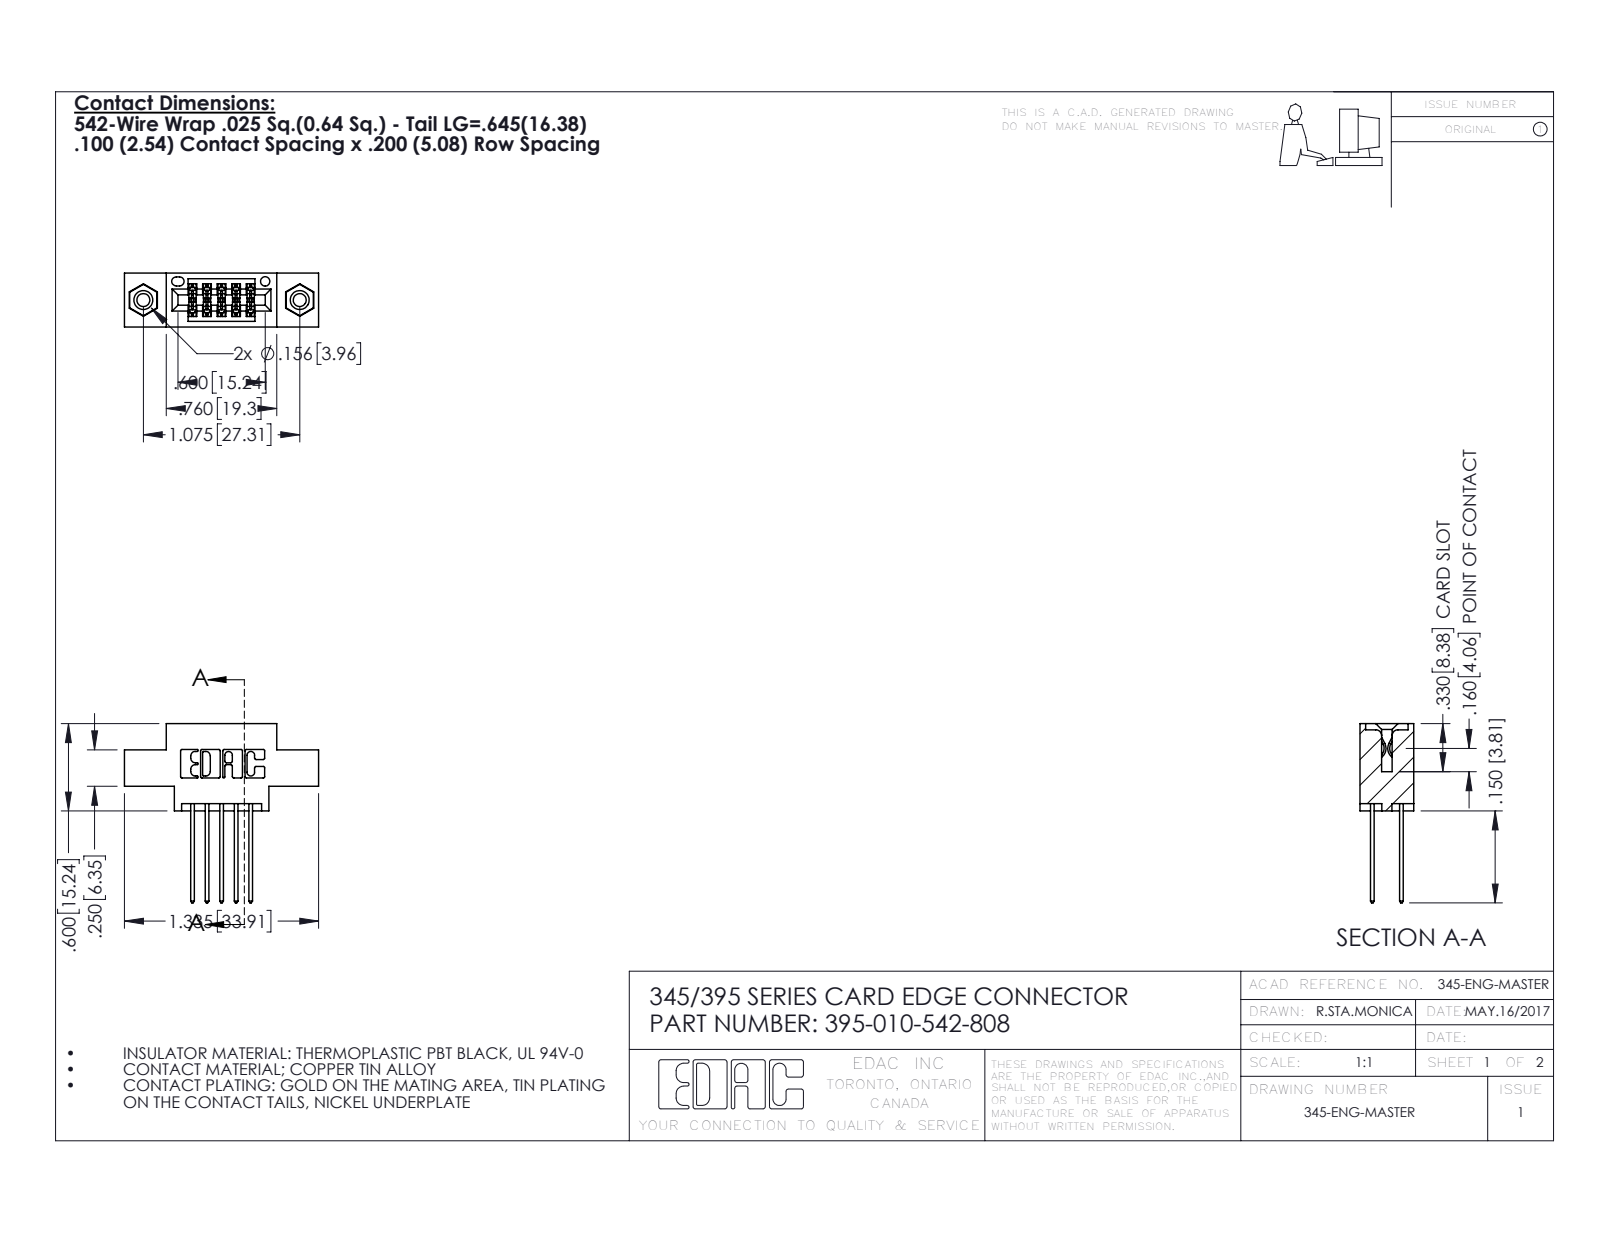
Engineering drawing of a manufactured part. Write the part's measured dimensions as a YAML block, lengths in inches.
part_name: "345-250-001_345-250-003-102; 345-292-001_345-293-142; 345 Part_0.170 Offset - 0.156 Dia-TI; 395-010-542-808"
step_written_by: "SolidWorks 2016 (CONFIG_CONTROL_DESIGN)"
units: inches
bodies: {solids: 13, faces: 690, planar: 446, cylindrical: 228, other: 16}
overall_size: [1.335, 1.232, 0.37]
volume: 0.176
surface_area: 6.062
round_holes:
  - {diameter: 0.089, count: 2}
  - {diameter: 0.125, count: 2}
  - {diameter: 0.156, count: 2}
  - {diameter: 0.064, count: 1}
round_bosses_or_shafts:
  - {diameter: 0.155, count: 2}
partial_cylinders:
  - {radius: 0.01, count: 22}
  - {radius: 0.006, count: 15}
  - {radius: 0.01, count: 10}
  - {radius: 0.007, count: 6}
  - {radius: 0.031, count: 6}
  - {radius: 0.026, count: 3}
  - {radius: 0.014, count: 2}
  - {radius: 0.019, count: 2}
face_to_face_distances: [0.2, 0.37, 0.072, 0.298, 0.1, 0.098, 0.272, 0.025, 0.225, 0.25]
hole_center_spacings: [0.27, 0.847, 1.075]
